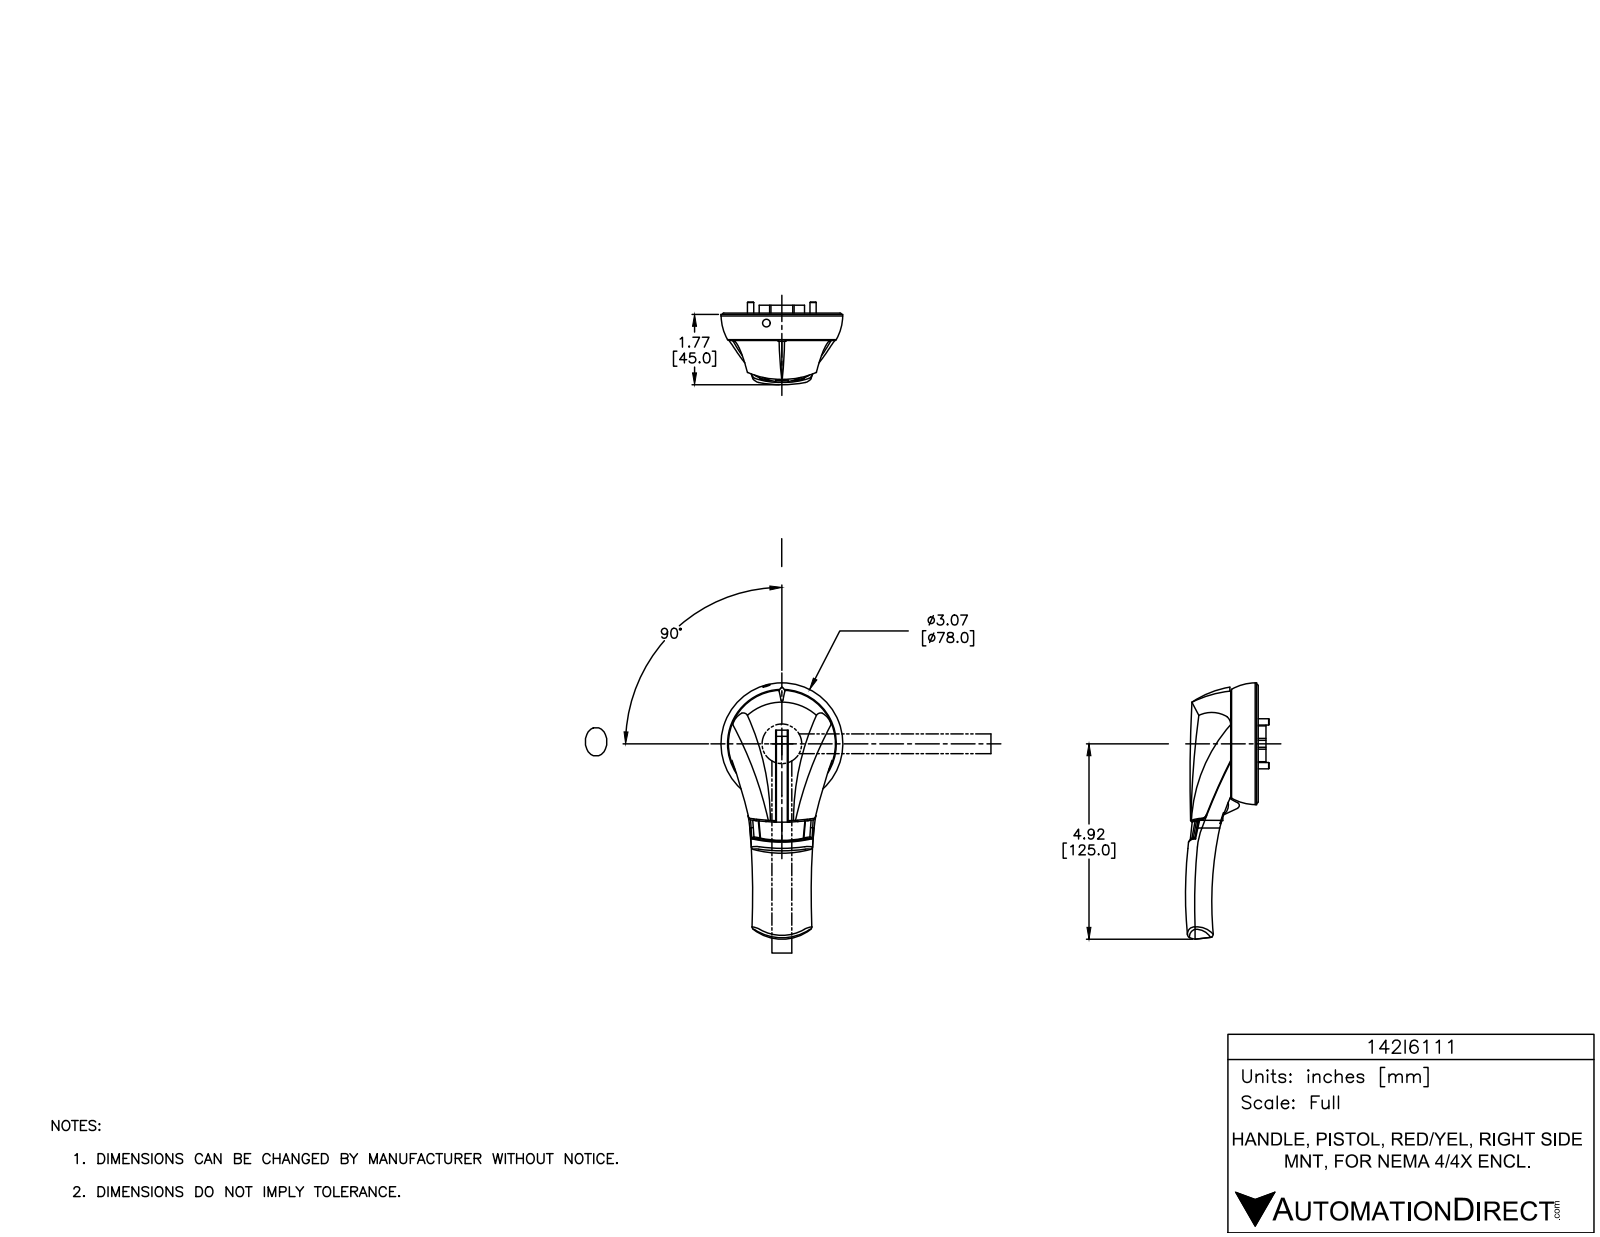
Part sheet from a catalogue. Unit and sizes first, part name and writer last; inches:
Units: inches
Overall size (bounding box): 6.458 × 3.07 × 2.079
Round holes (diameter × count): ⌀0.157 ×6, ⌀0.339 ×4, ⌀0.425 ×4, ⌀0.03 ×3, ⌀0.169 ×2, ⌀0.362 ×2, ⌀0.118 ×1, ⌀0.189 ×1, ⌀2.992 ×1
Round bosses / shafts (diameter × count): ⌀0.02 ×11, ⌀0.335 ×4, ⌀0.315 ×4, ⌀0.089 ×3, ⌀0.069 ×3, ⌀0.228 ×2, ⌀2.819 ×1, ⌀2.701 ×1
Partial cylindrical surfaces — rounded edges, fillets, slot ends (radius × count): R0.01 ×221, R0.015 ×20, R0.034 ×20, R0.03 ×15, R0.039 ×4, R0.025 ×3, R5.437 ×3, R0.079 ×2
Main face-to-face distances: 0.024, 0.701, 0.713, 0.689, 0.035, 0.102, 0.276, 0.173, 0.244, 0.047
Hole centre spacings: 0.961, 0.309, 0.669, 1.098, 1.102, 1.203, 1.575, 1.881
Volume: 9.514 in³ · Surface area: 87.32 in²
Bodies: 8 solids, 1516 faces (810 planar, 548 cylindrical, 158 other)
Part name (STEP PRODUCT): 142I6111
STEP written by: SolidWorks 2015 (AUTOMOTIVE_DESIGN)
